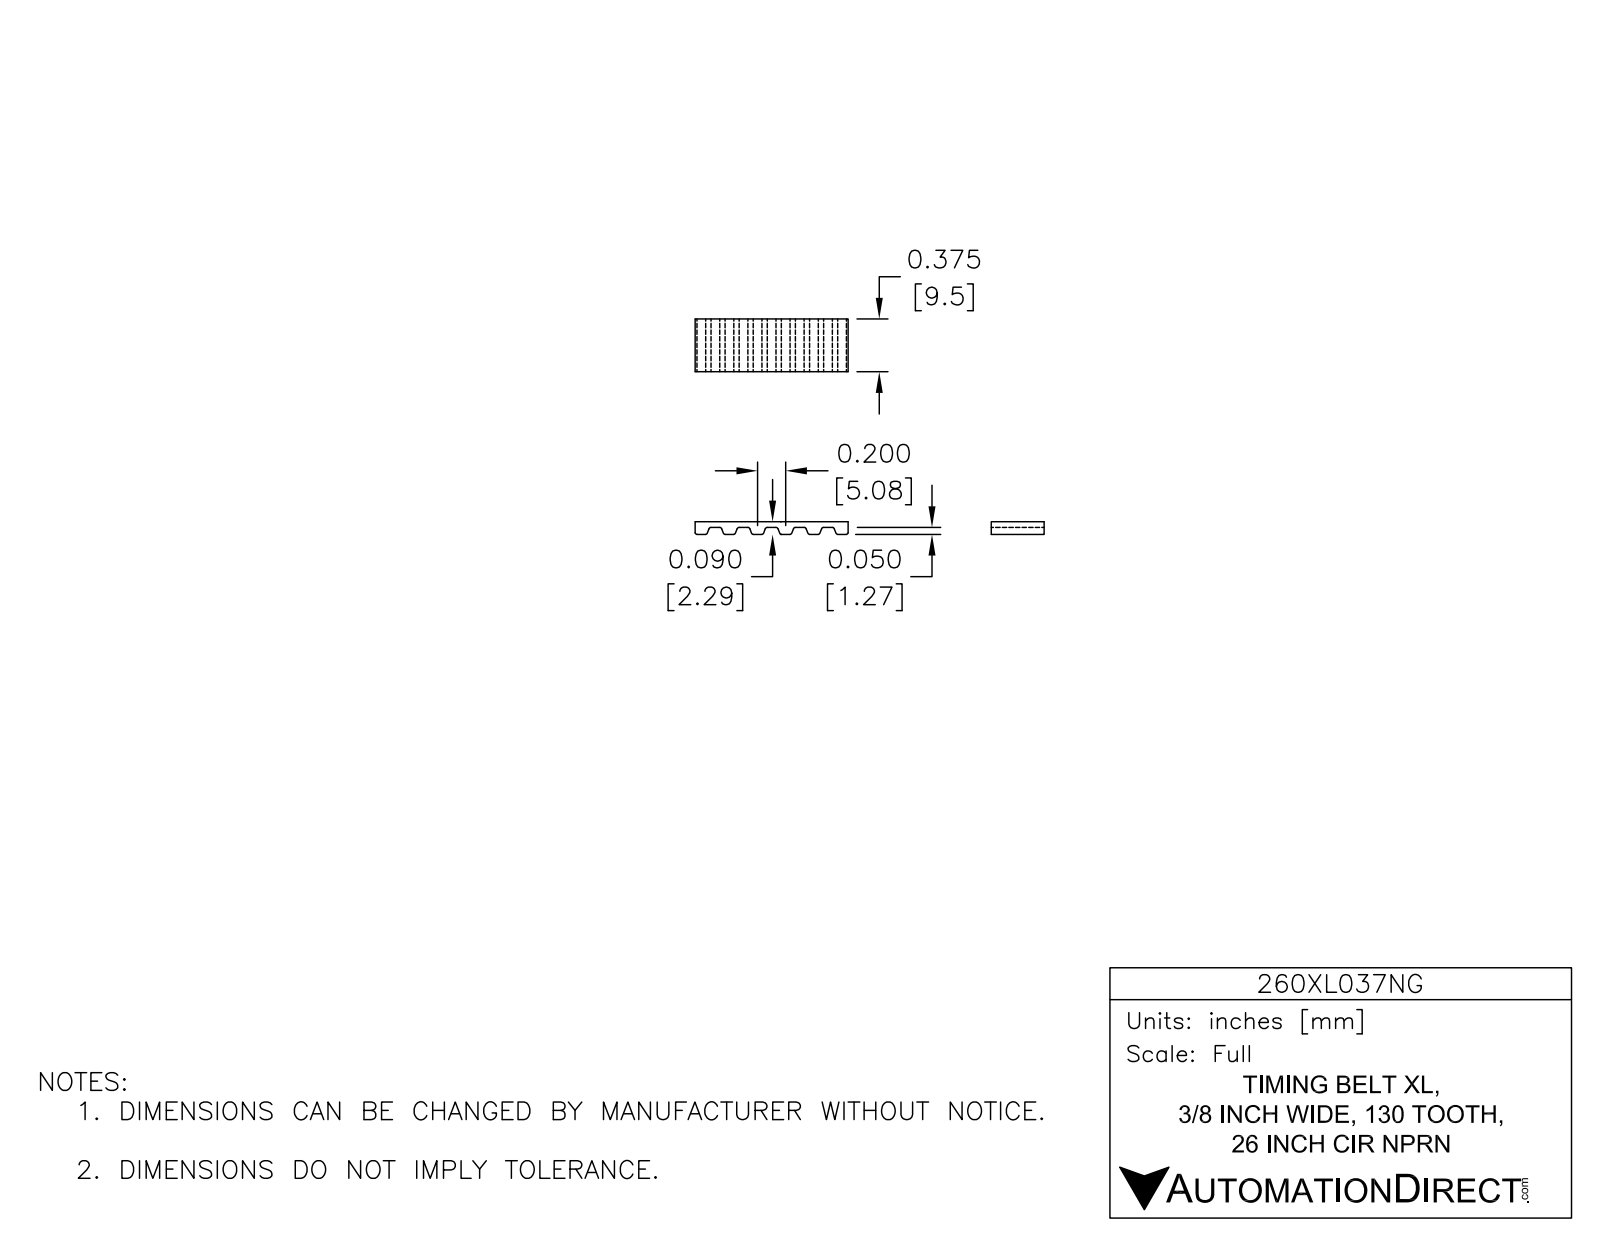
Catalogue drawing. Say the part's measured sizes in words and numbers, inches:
The part is named "260XL037NG". Its 3-D file was written by "SolidWorks 2014 (AUTOMOTIVE_DESIGN)". It is 1 solid with 1076 faces: 478 planar, 598 cylindrical and 0 other. Overall it measures 11.288 by 3 by 0.375 inches. Its volume is 0.531 cubic inches and its surface area 24.93 square inches. Partial cylindrical surfaces (rounded edges, fillets, slot ends): 520 of radius 0.015, 2 of radius 1.46, 2 of radius 1.5. The main face-to-face distances are 3, 0.04, 2.96, 2.92, 0.375, 0.09, 2.91, 0.05, 2.87, 2.82.
